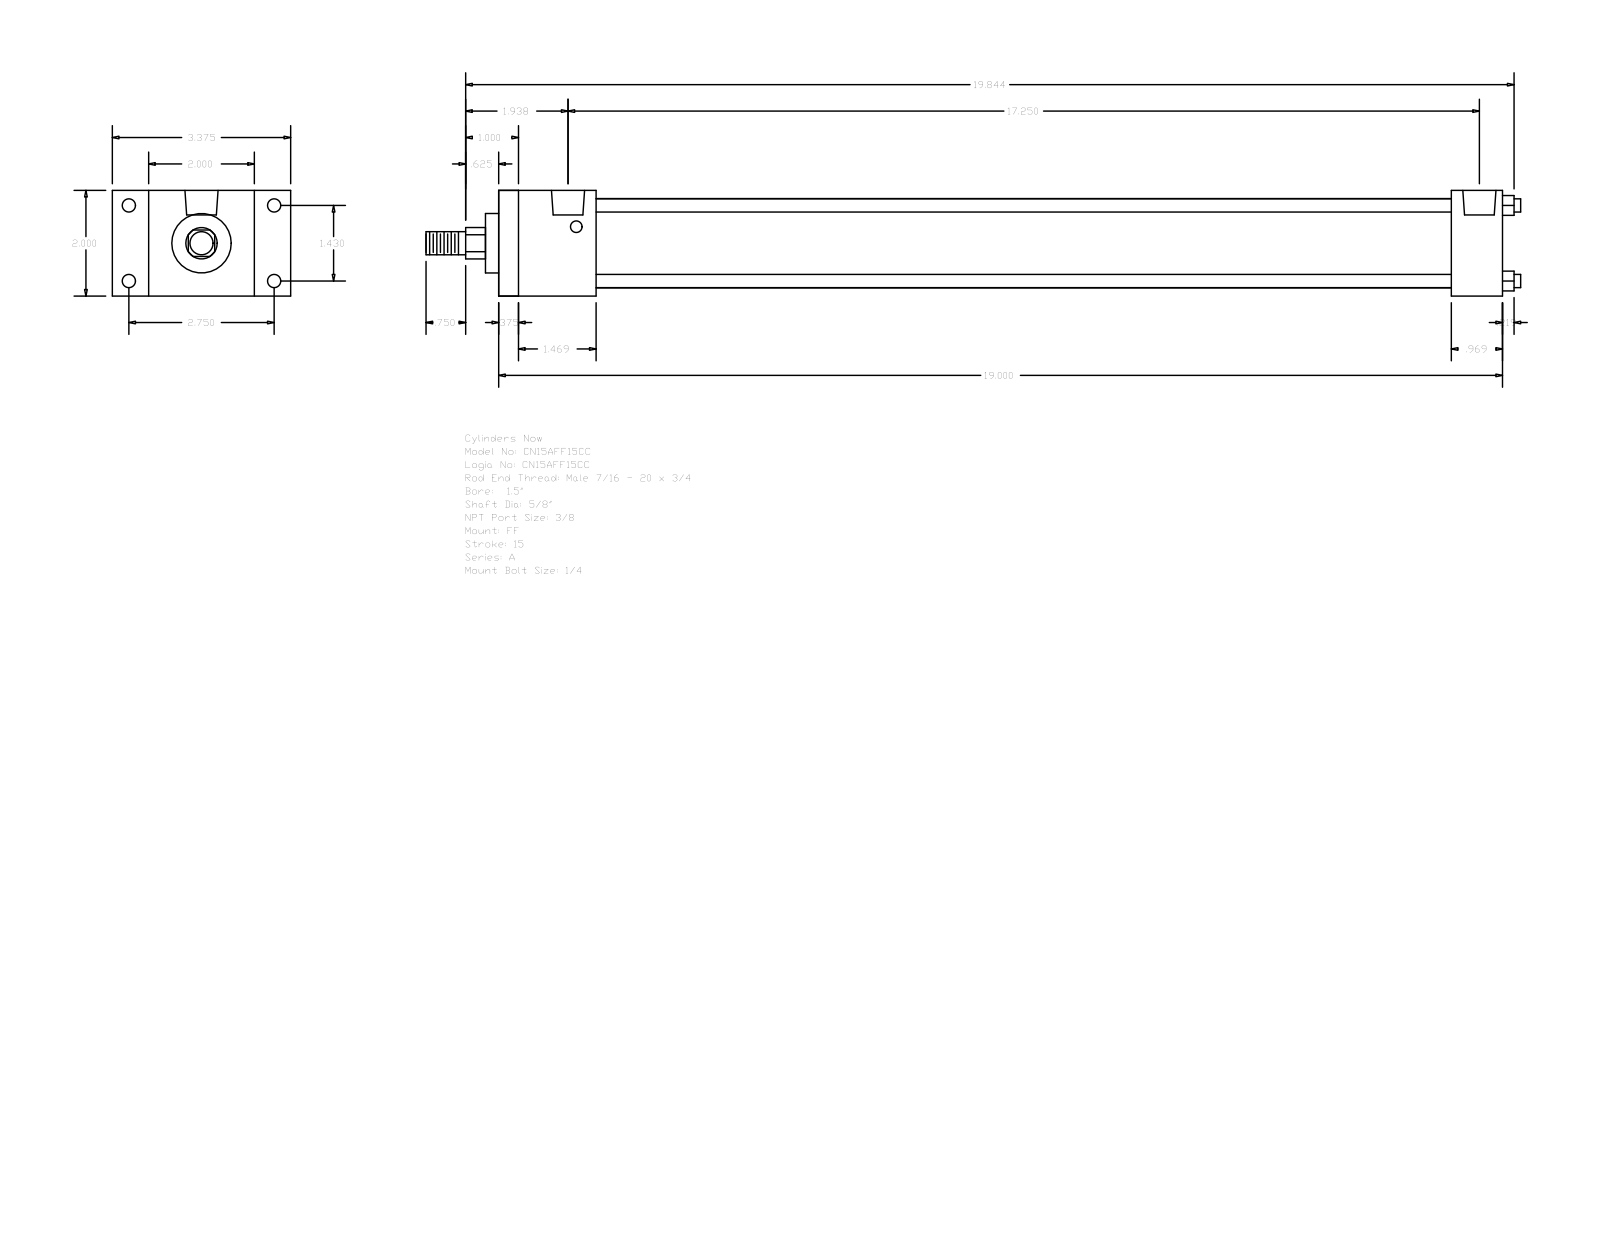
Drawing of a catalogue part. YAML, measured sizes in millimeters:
part_name: "A_FF__0150_0.625"
step_written_by: "GSSL Pune (CONFIG_CONTROL_DESIGN)"
units: millimeters
bodies: {solids: 0, faces: 92, planar: 64, cylindrical: 28, other: 0}
overall_size: [526.26, 85.72, 50.8]
round_holes:
  - {diameter: 5.56, count: 4}
  - {diameter: 6.35, count: 4}
  - {diameter: 15.93, count: 2}
round_bosses_or_shafts:
  - {diameter: 6.35, count: 4}
  - {diameter: 42.93, count: 1}
  - {diameter: 28.57, count: 1}
  - {diameter: 15.88, count: 1}
  - {diameter: 11.11, count: 1}
partial_cylinders:
  - {radius: 7.54, count: 1}
face_to_face_distances: [50.8, 482.6, 9.52, 473.08, 46.83, 457.99, 37.31, 448.47, 411.16, 435.77]
hole_center_spacings: [3.97, 36.32, 69.84, 78.72, 430.21, 434.18, 438.15]
